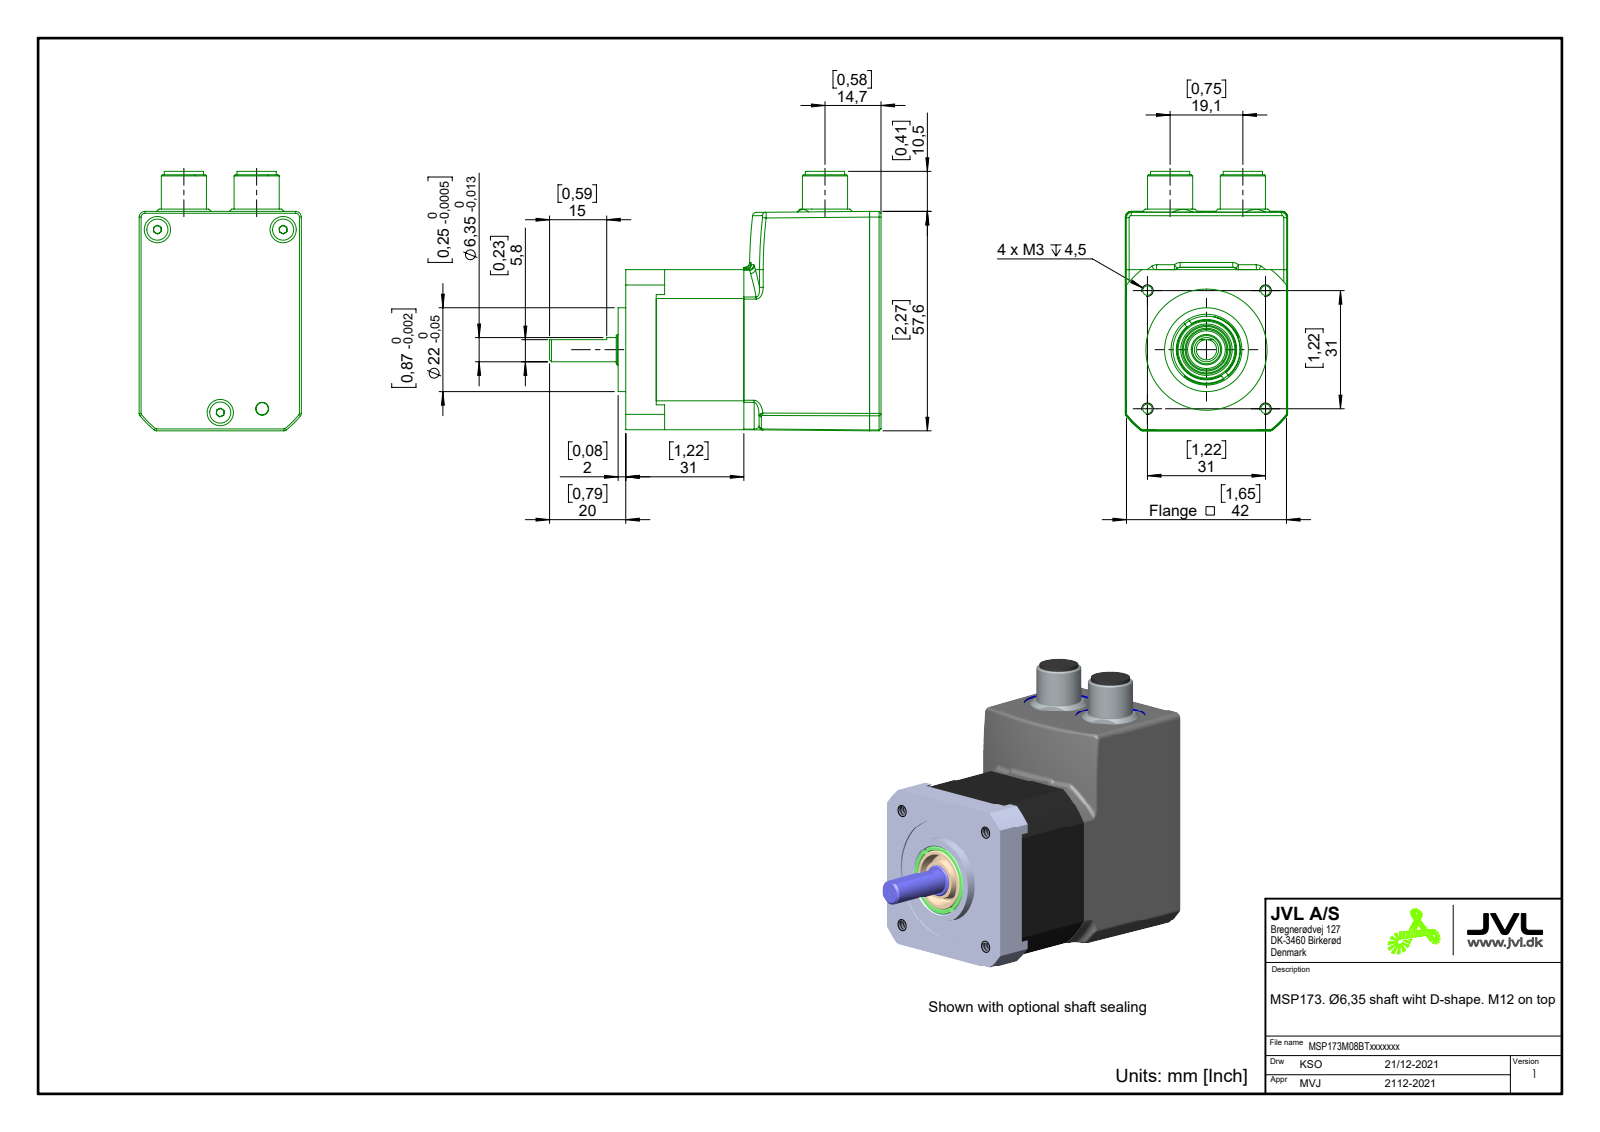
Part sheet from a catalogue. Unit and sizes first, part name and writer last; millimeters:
Units: millimetres
Overall size (bounding box): 87 × 68.08 × 42.58
Round holes (diameter × count): ⌀2.5 ×4, ⌀3.3 ×3, ⌀18.4 ×2, ⌀2.8 ×1, ⌀3.4 ×1, ⌀9 ×1, ⌀31.8 ×1
Round bosses / shafts (diameter × count): ⌀5.54 ×3, ⌀3 ×3, ⌀15.1 ×2, ⌀11.85 ×2, ⌀10.3 ×2, ⌀22 ×1, ⌀15.5 ×1, ⌀13.9 ×1
Partial cylindrical surfaces — rounded edges, fillets, slot ends (radius × count): R1 ×13, R1.5 ×2, R8.8 ×1, R24.92 ×1, R25.5 ×1, R27 ×1, R27.29 ×1, R80 ×1
Main face-to-face distances: 42, 67, 2, 66.5, 0.5, 42.29, 1.5, 65, 2.5, 4
Hole centre spacings: 21.92, 31, 35.56, 15.53, 16.03, 35.78, 43.84, 47.01
Volume: 140 069 mm³ · Surface area: 19 765 mm²
Bodies: 5 solids, 328 faces (134 planar, 71 cylindrical, 123 other)
Part name (STEP PRODUCT): MSP173M08BTxxxxxxx
STEP written by: FreeCAD (AUTOMOTIVE_DESIGN)
